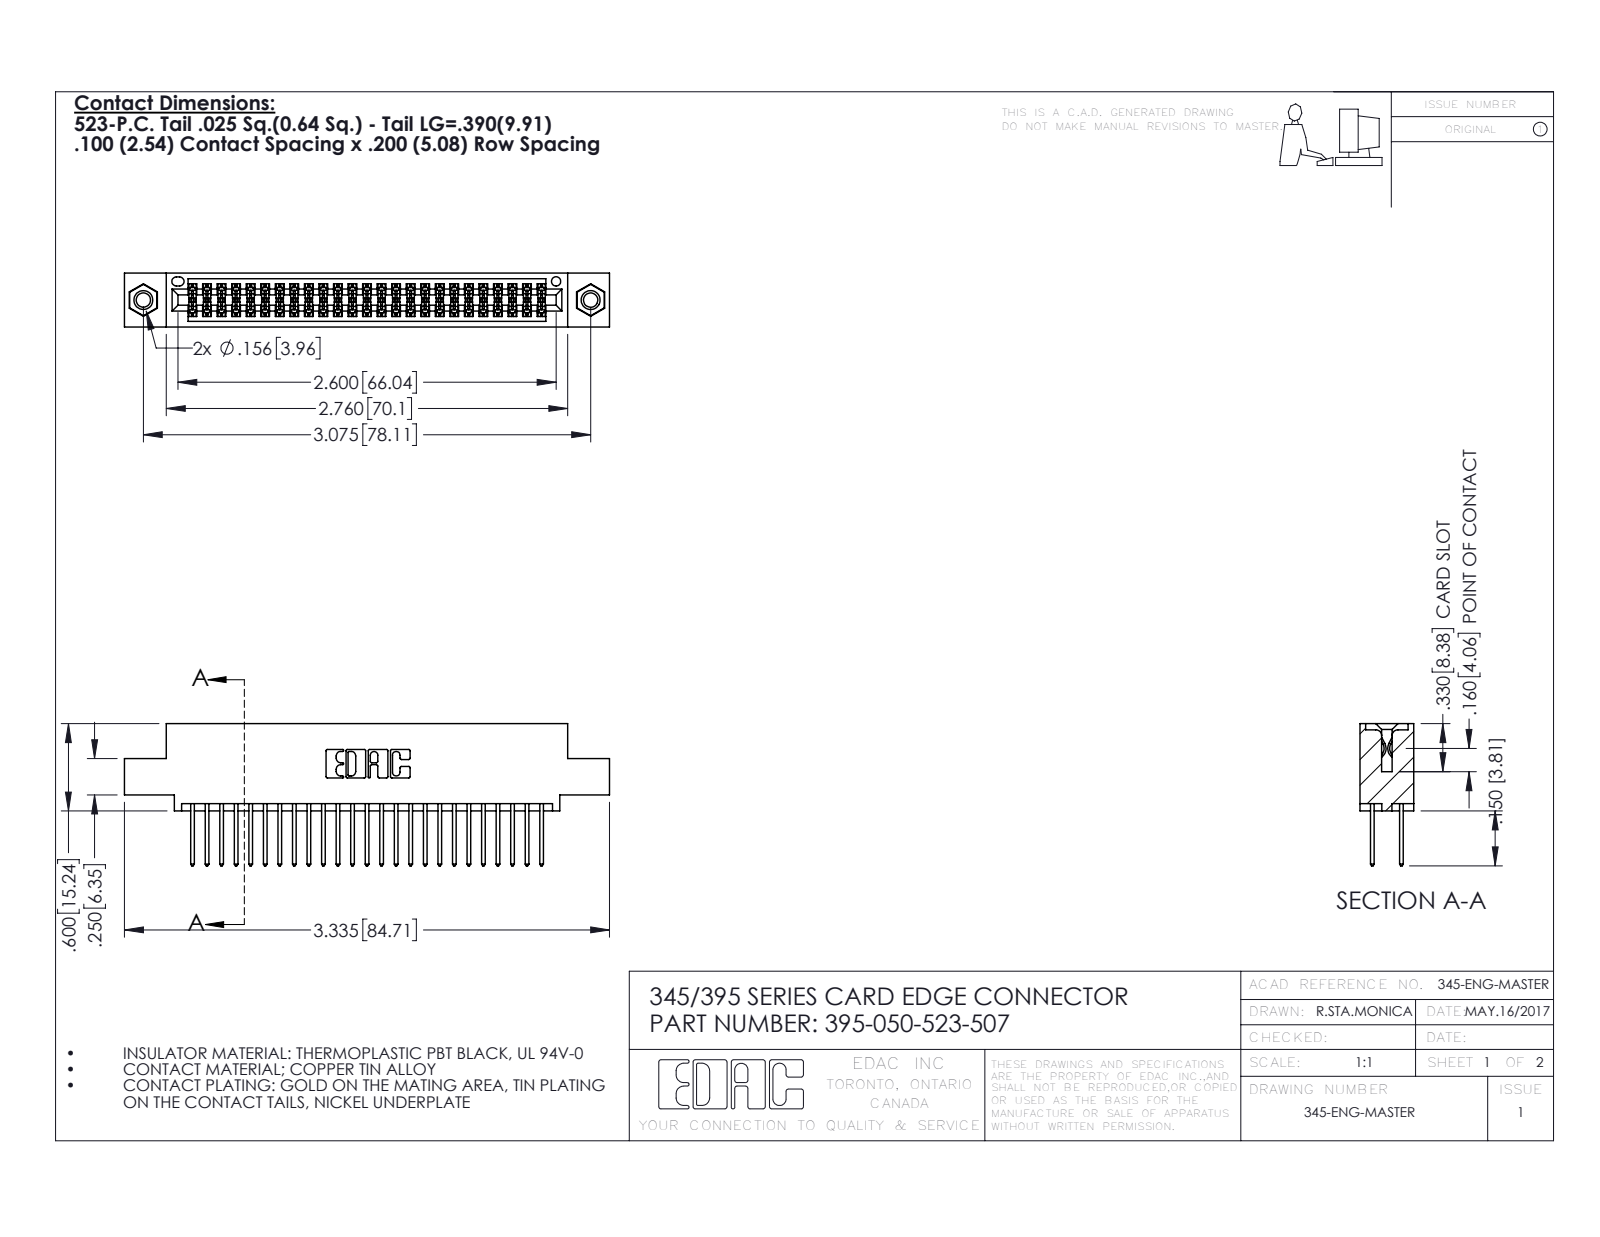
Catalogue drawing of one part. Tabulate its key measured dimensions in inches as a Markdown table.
| quantity | value |
| --- | --- |
| part name | 345 Part_0.110 Offset - 0.156 Dia-TI; 345-292-001_345-293-123; 345-250-001_345-250-005-103; 395-050-523-507 |
| STEP written by | SolidWorks 2016 (CONFIG_CONTROL_DESIGN) |
| units | inches |
| bodies | 53 solids, 2690 faces (1766 planar, 908 cylindrical, 16 other) |
| overall size | 3.335 × 0.977 × 0.37 |
| volume | 0.493 in³ |
| surface area | 18.92 in² |
| round holes (diameter × count) | 0.098 × 2, 0.125 × 2, 0.156 × 2, 0.064 × 1 |
| round bosses / shafts (diameter × count) | 0.155 × 2 |
| partial cylindrical surfaces (radius × count) | 0.006 × 75, 0.01 × 50, 0.01 × 22, 0.007 × 6, 0.031 × 6, 0.026 × 3, 0.014 × 2, 0.019 × 2 |
| main face-to-face distances | 0.072, 0.298, 0.2, 0.098, 0.272, 0.025, 0.37, 0.225, 0.175, 0.149 |
| hole center spacings | 0.27, 2.84, 3.075 |
